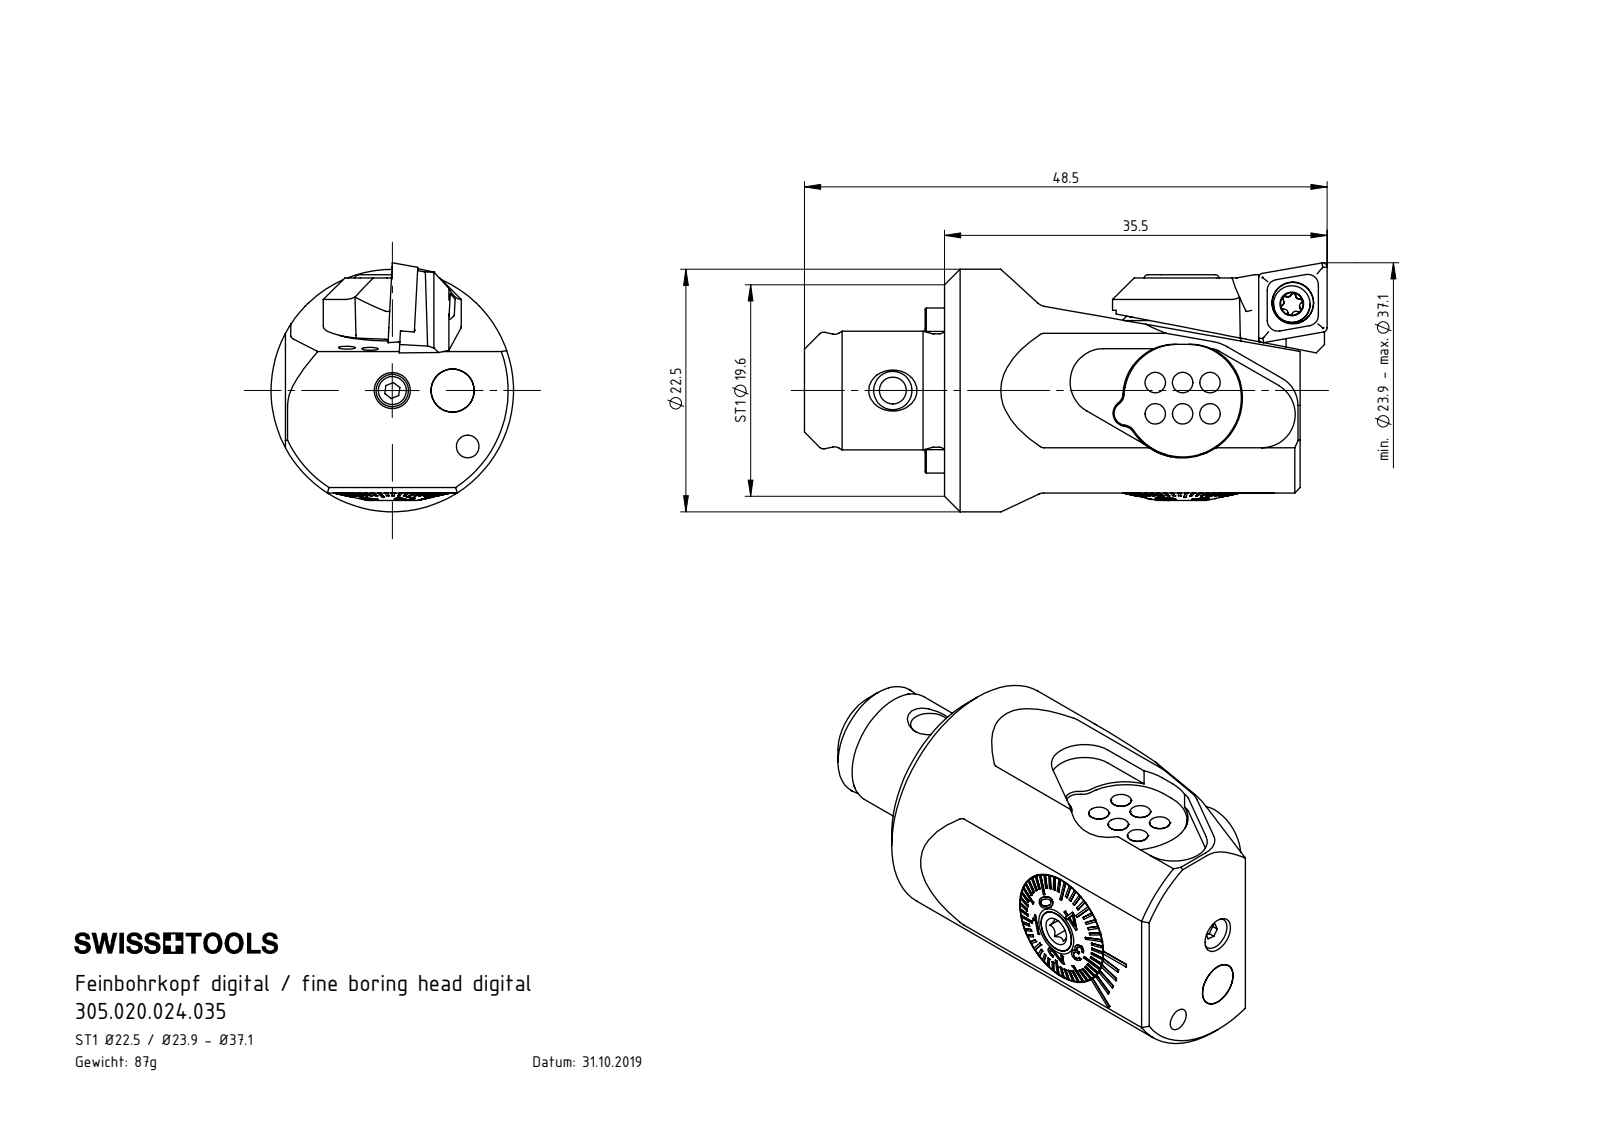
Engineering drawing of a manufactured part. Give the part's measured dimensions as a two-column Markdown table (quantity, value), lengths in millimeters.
| quantity | value |
| --- | --- |
| part name | F20-BG2.008.009_A; F20-BG2.007.006_A; F20-BG1.DA3.011_A_Standart; F20-BG1.DA4.011_verstellbar (+8 more) |
| STEP written by | SolidWorks 2017 (AUTOMOTIVE_DESIGN) |
| units | millimeters |
| bodies | 16 solids, 676 faces (398 planar, 90 cylindrical, 188 other) |
| overall size | 46 × 22.5 × 22.5 |
| volume | 10 784 mm³ |
| surface area | 7 427 mm² |
| round holes (diameter × count) | 2.1 × 4, 1.5 × 2, 1.8 × 2, 3 × 2, 3.3 × 2, 1.08 × 1, 1.9 × 1, 2.5 × 1, 4 × 1, 4.2 × 1, 4.5 × 1, 5.75 × 1 |
| round bosses / shafts (diameter × count) | 1.9 × 6, 11 × 2, 4 × 2, 3.95 × 2, 22.5 × 1, 10.98 × 1, 10.85 × 1, 10.8 × 1 |
| partial cylindrical surfaces (radius × count) | 0.3 × 6, 1.1 × 3, 1.2 × 3, 5.55 × 3, 1.25 × 2, 1.48 × 2, 2 × 2, 3.1 × 2 |
| main face-to-face distances | 33, 3.7, 1.5, 1.4, 0.8, 2.9, 1.72, 2.8, 1.47, 2.5 |
| hole center spacings | 6.65, 8.69, 1, 5.38, 5.6, 7.15, 8.71, 13.3 |
